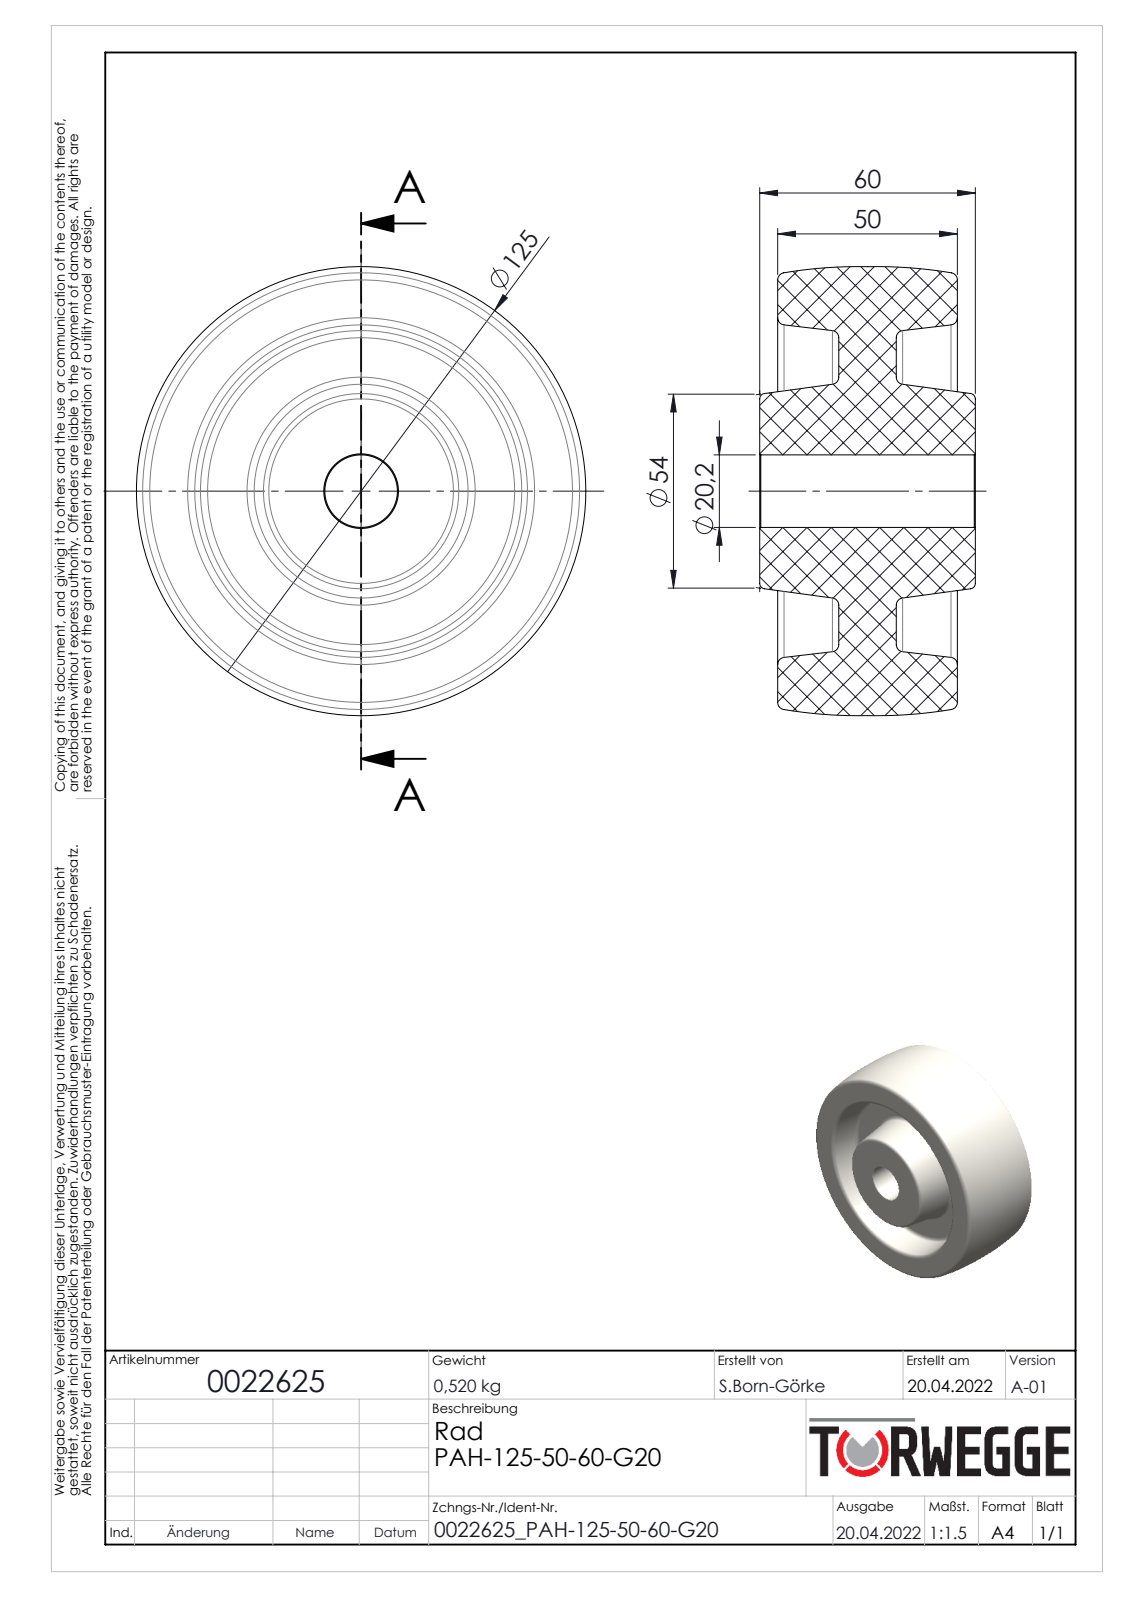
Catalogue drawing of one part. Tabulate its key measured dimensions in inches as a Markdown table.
| quantity | value |
| --- | --- |
| part name | 0022625 |
| STEP written by | SolidWorks 2020 (AUTOMOTIVE_DESIGN) |
| units | inches |
| bodies | 1 solid, 44 faces (6 planar, 2 cylindrical, 36 other) |
| overall size | 4.923 × 4.923 × 2.362 |
| volume | 28.93 in³ |
| surface area | 92.45 in² |
| round holes (diameter × count) | 0.795 × 1 |
| main face-to-face distances | 0.669, 1.299, 1.969, 0.197, 0.866, 1.496, 2.165, 0.63, 2.362 |
